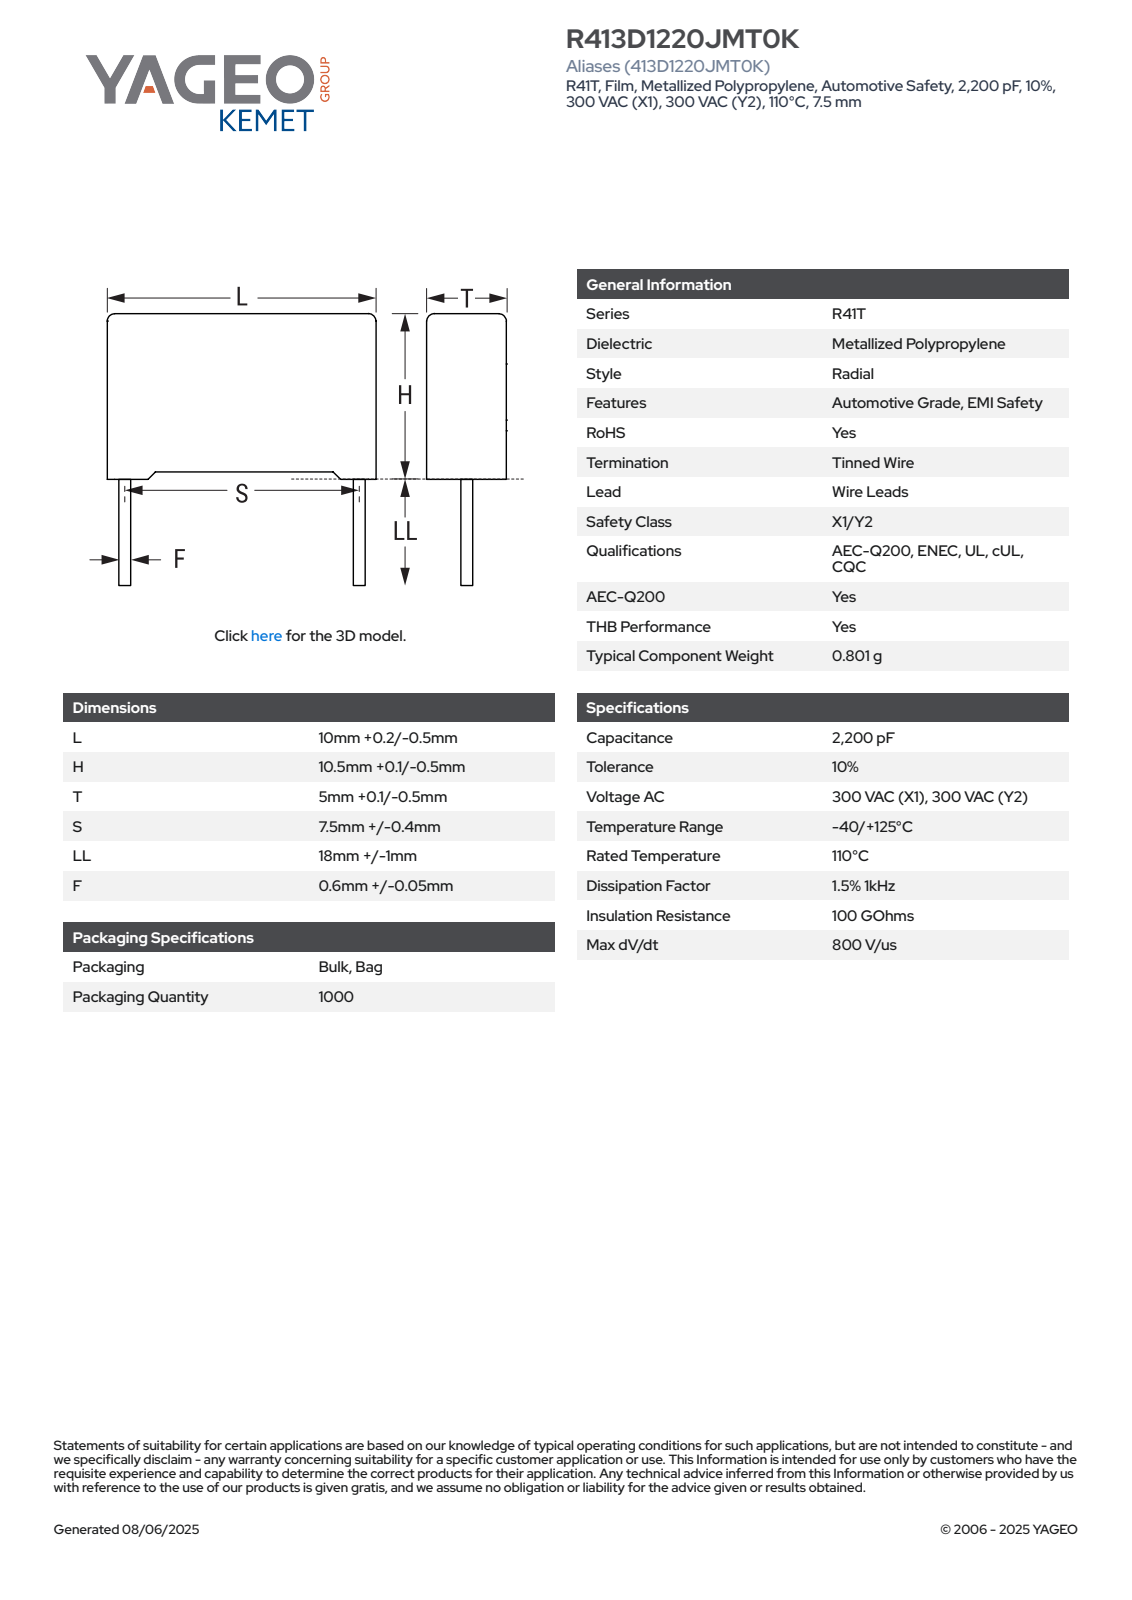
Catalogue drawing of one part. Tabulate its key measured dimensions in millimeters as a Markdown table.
| quantity | value |
| --- | --- |
| part name | CFR_RB2_10X10.5X5_L10.2H10.6T5.1S7.5LL19F0.65 |
| STEP written by | SolidWorks 2021 (AUTOMOTIVE_DESIGN) |
| units | millimeters |
| bodies | 4 solids, 85 faces (77 planar, 8 cylindrical, 0 other) |
| overall size | 29.6 × 10.2 × 5.11 |
| volume | 530 mm³ |
| surface area | 525 mm² |
| round bosses / shafts (diameter × count) | 0.65 × 2 |
| partial cylindrical surfaces (radius × count) | 0.5 × 4 |
| main face-to-face distances | 5.1, 10.2, 9.85, 0.34, 4.76, 0.75, 10.6, 9.86, 4.42, 9.52 |
